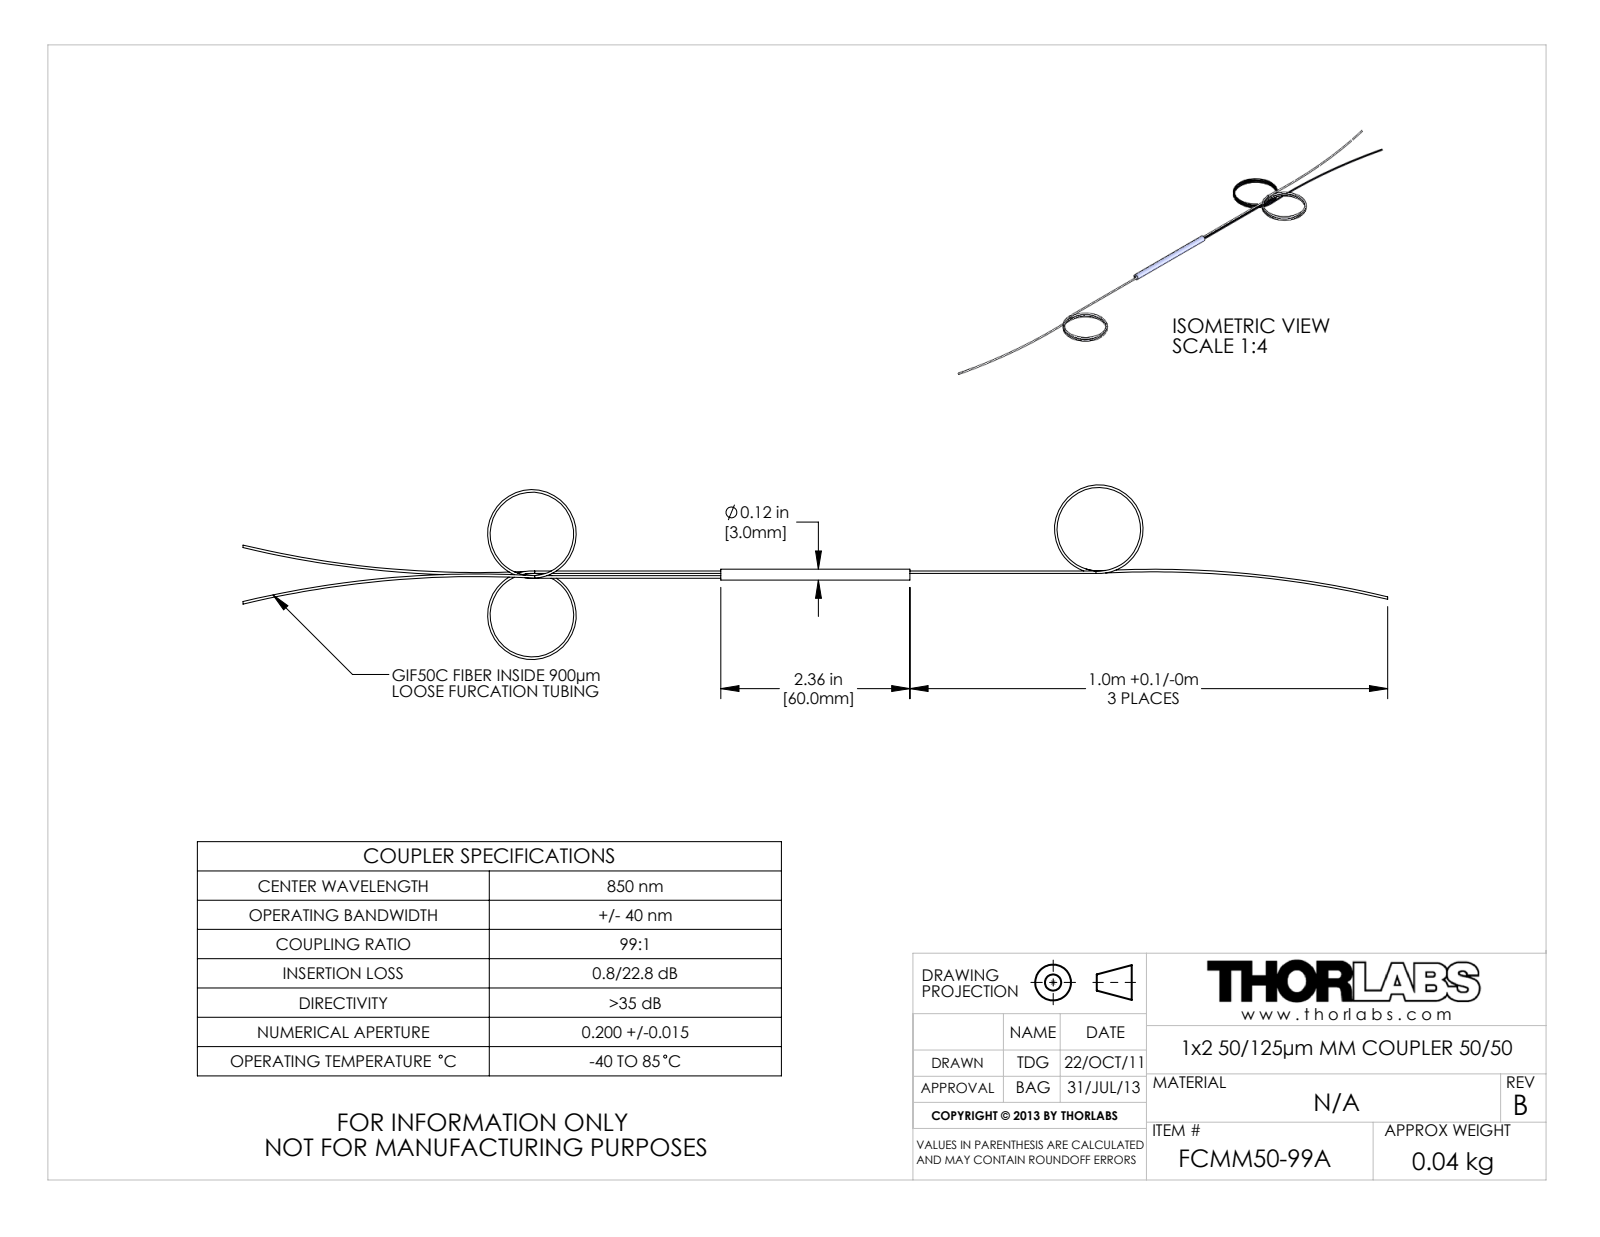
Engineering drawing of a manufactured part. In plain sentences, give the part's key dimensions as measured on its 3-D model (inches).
The part is named "13899-E0W". Its 3-D file was written by "SolidWorks 2012 (CONFIG_CONTROL_DESIGN)". It is 4 solids with 46 faces: 10 planar, 18 cylindrical and 18 other. Overall it measures 15.74 by 2.4 by 0.272 inches. Its volume is 0.068 cubic inches and its surface area 8.722 square inches. Round holes: 2 of diameter 0.039, 1 of diameter 0.13. Round bosses or shafts: 2 of diameter 0.035, 1 of diameter 0.15. The main face-to-face distances are 2.594, 2.598, 2.591, 6.571, 6.575, 9.165, 9.169, 7.949, 1.22, 1.378. The hole center spacings are 0.033, 0.065.
